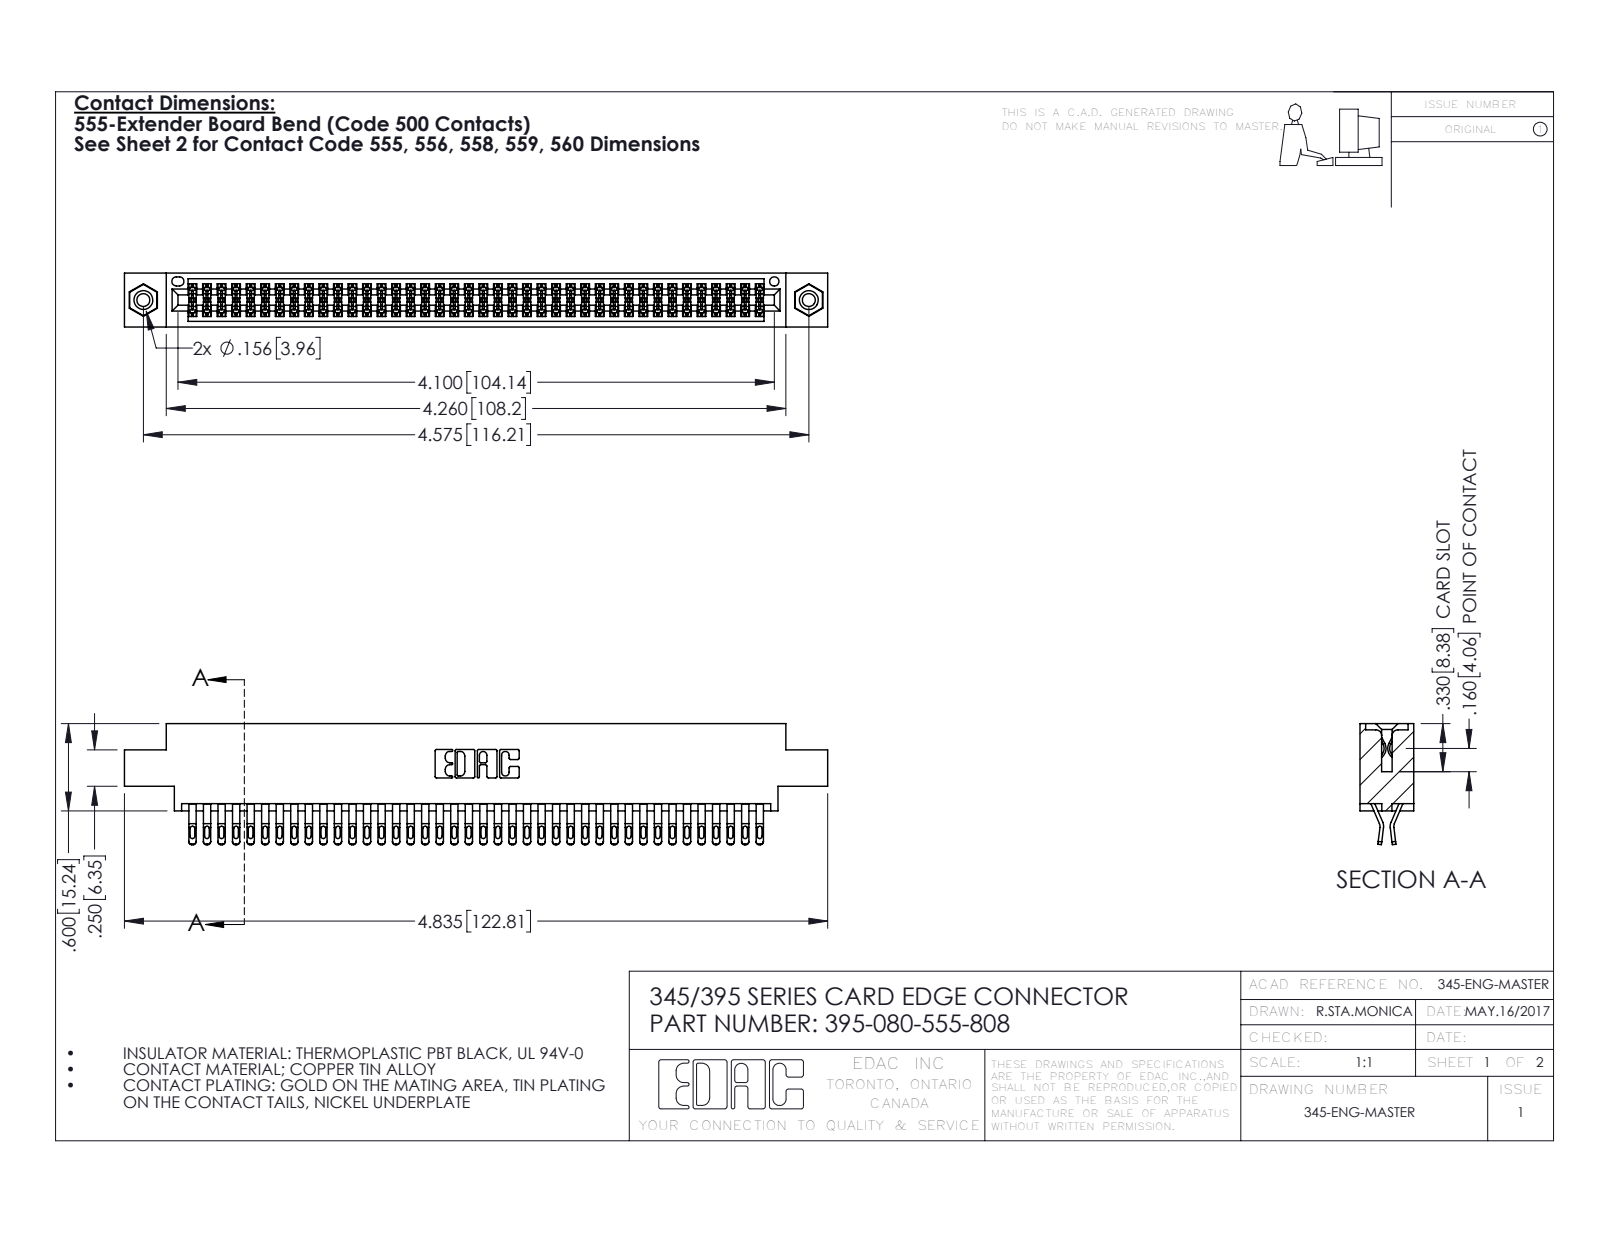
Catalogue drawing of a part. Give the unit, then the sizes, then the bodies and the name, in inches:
Units: inches
Overall size (bounding box): 4.835 × 0.832 × 0.37
Round holes (diameter × count): ⌀0.089 ×2, ⌀0.125 ×2, ⌀0.156 ×2, ⌀0.064 ×1
Round bosses / shafts (diameter × count): ⌀0.155 ×2
Partial cylindrical surfaces — rounded edges, fillets, slot ends (radius × count): R0.016 ×200, R0.02 ×160, R0.006 ×120, R0.01 ×22, R0.007 ×6, R0.031 ×6, R0.026 ×3, R0.01 ×2
Main face-to-face distances: 0.072, 0.298, 0.37, 0.025, 0.2, 0.098, 0.272, 0.225, 0.175, 0.149
Hole centre spacings: 0.27, 4.339, 4.575
Volume: 0.734 in³ · Surface area: 28.98 in²
Bodies: 83 solids, 4670 faces (2596 planar, 2058 cylindrical, 16 other)
Part name (STEP PRODUCT): 345-250-001_345-250-003-102; 345-292-001_555 Tail; 345 Part_0.170 Offset - 0.156 Dia-TI; 395-080-555-808
STEP written by: SolidWorks 2016 (CONFIG_CONTROL_DESIGN)
